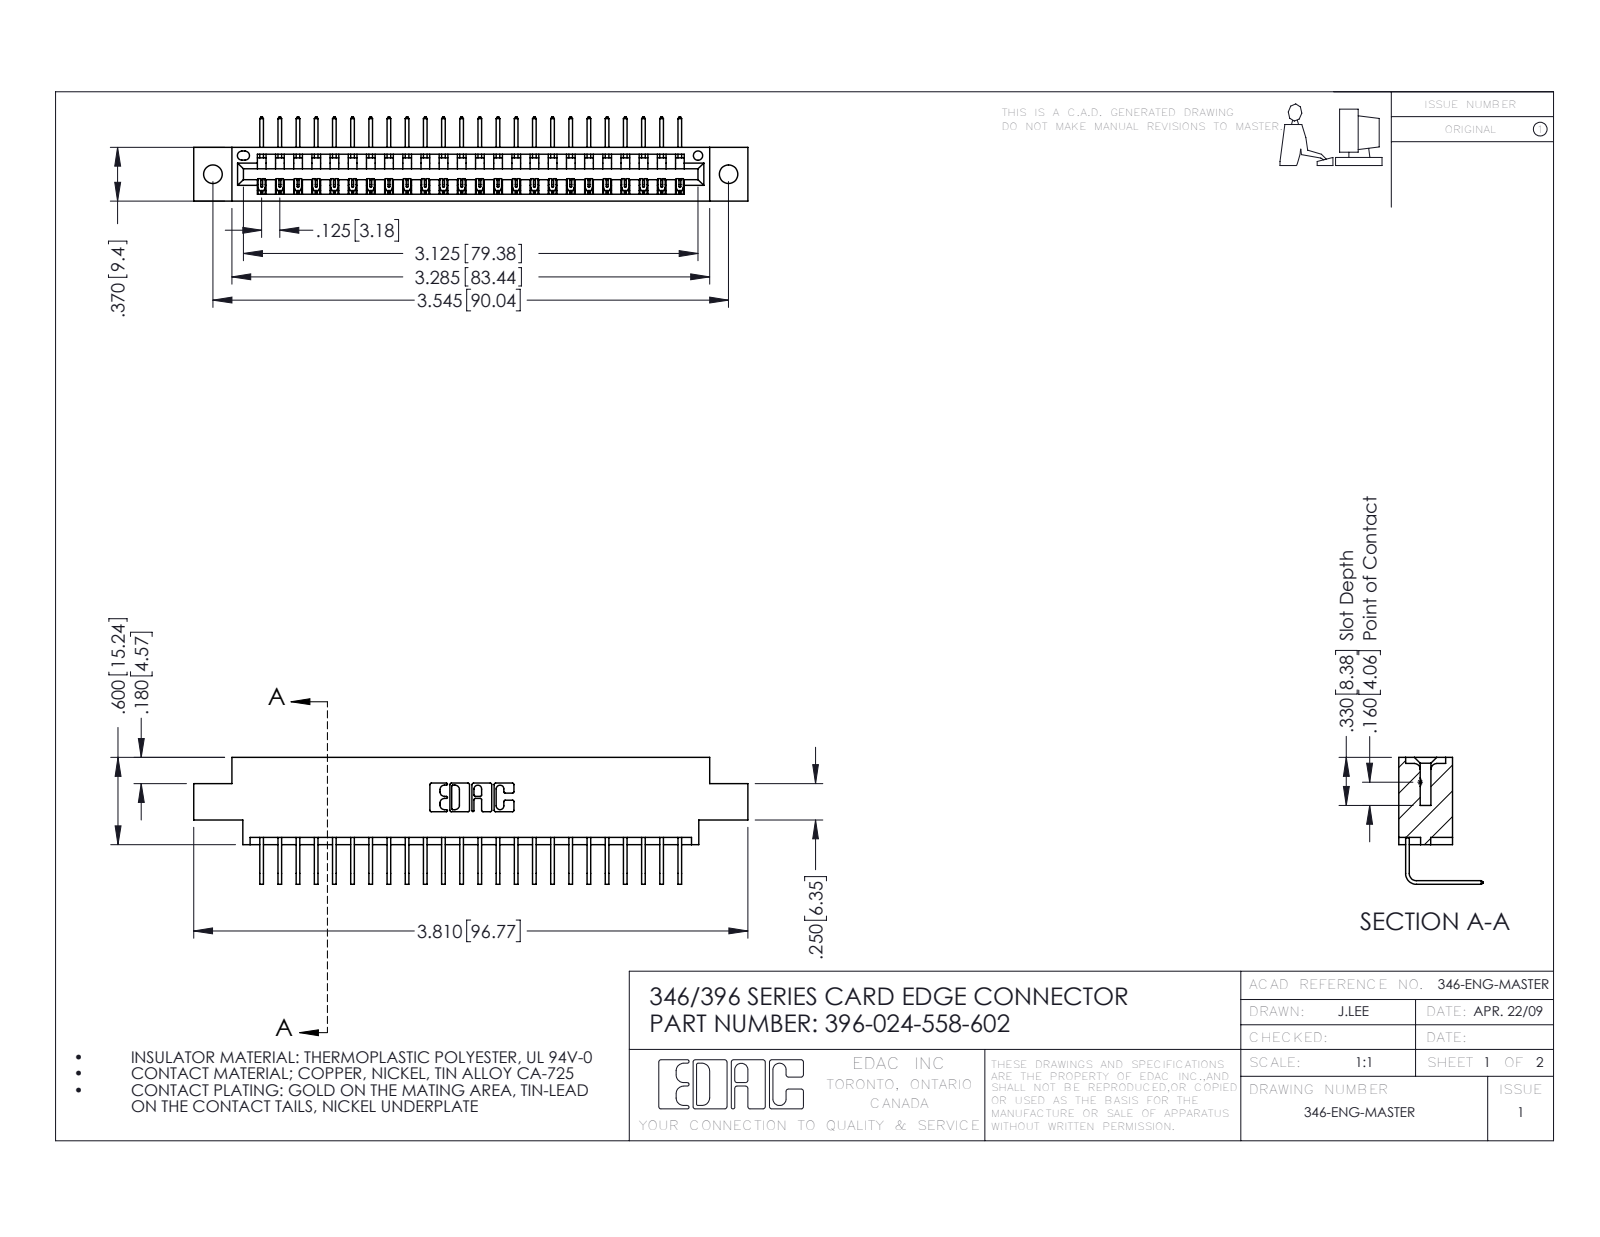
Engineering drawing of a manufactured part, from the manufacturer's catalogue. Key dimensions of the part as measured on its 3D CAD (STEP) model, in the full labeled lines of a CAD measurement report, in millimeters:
Part name (STEP PRODUCT): 346 Part_0.170 Offset - 0.128 Dia; 396-024-558-602; 345-292-001_558 Tail - 2
STEP written by: SolidWorks 2016 (CONFIG_CONTROL_DESIGN)
Units: millimetres
Bodies: 25 solids, 1566 faces (1088 planar, 478 cylindrical, 0 other)
Overall size (bounding box): 96.8 × 22.2 × 14.7
Volume: 9 030 mm³ · Surface area: 11 460 mm²
Round holes (diameter × count): ⌀3.3 ×2, ⌀1.6 ×1
Partial cylindrical surfaces — rounded edges, fillets, slot ends (radius × count): R0.2 ×48, R0.3 ×22, R0.2 ×6, R0.8 ×6, R0.7 ×3, R0.8 ×2, R1 ×2, R0.4 ×1
Main face-to-face distances: 8.2, 1.2, 9.4, 6.4, 7.6, 0.6, 1.8, 3.8, 5.6, 2.5
Hole centre spacings: 6.2, 84.8, 90
